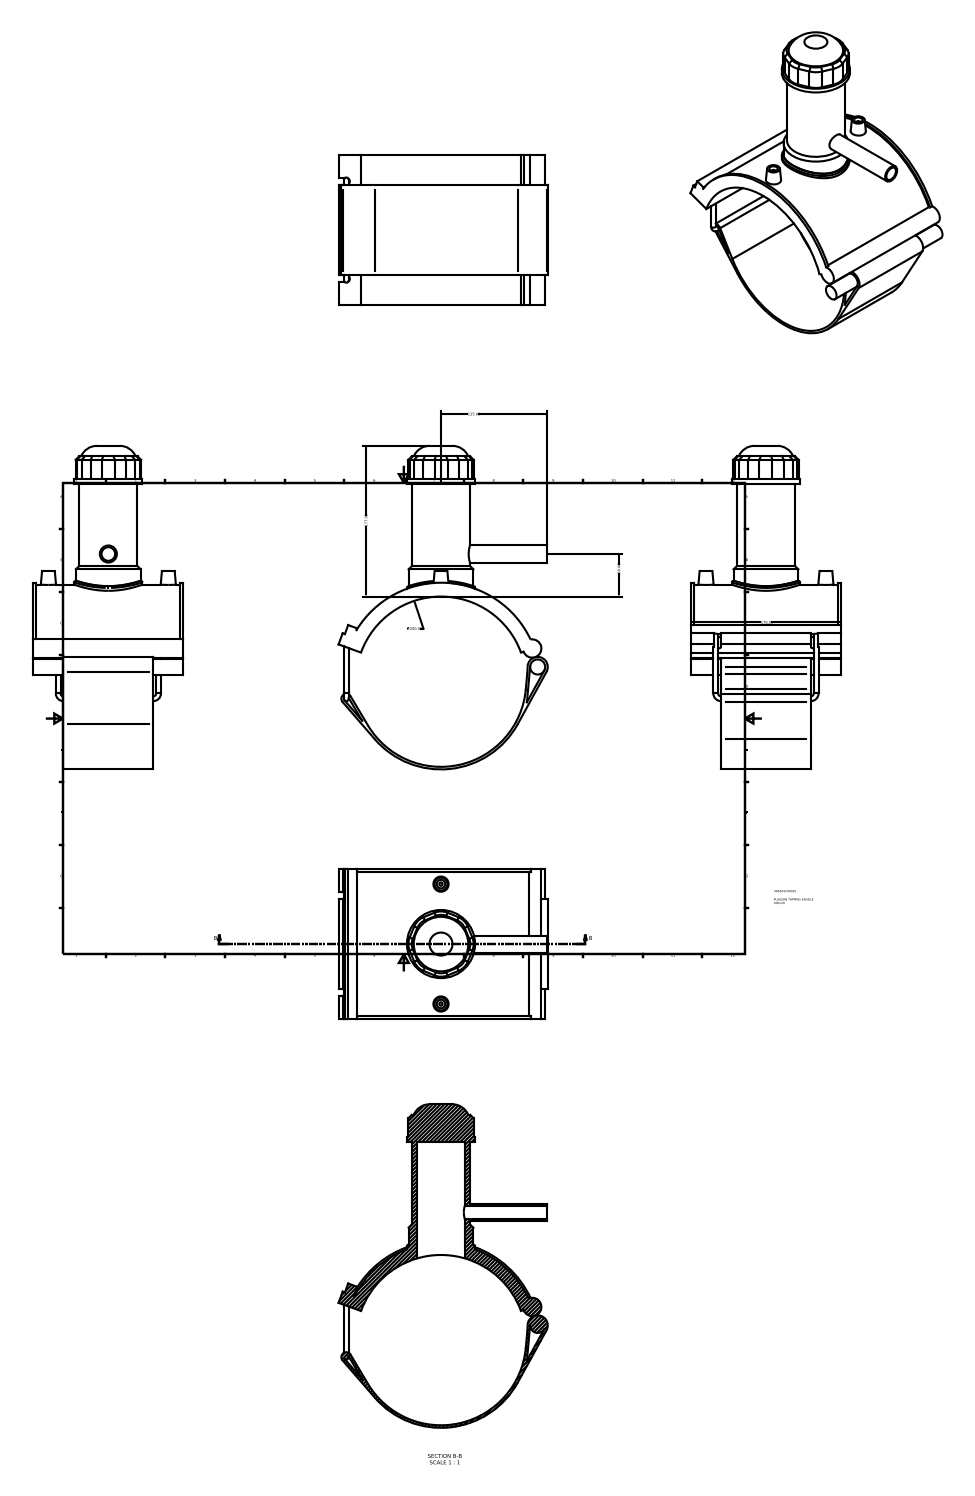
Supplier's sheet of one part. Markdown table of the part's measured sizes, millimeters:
| quantity | value |
| --- | --- |
| part name | 496304200020 |
| STEP written by | Autodesk Inventor 2015 (AUTOMOTIVE_DESIGN) |
| units | millimeters |
| bodies | 1 solid, 121 faces (68 planar, 38 cylindrical, 15 other) |
| overall size | 380 × 245.66 × 176 |
| volume | 1 264 000 mm³ |
| surface area | 299 248 mm² |
| round holes (diameter × count) | 10 × 2, 16 × 1, 56 × 1 |
| round bosses / shafts (diameter × count) | 5.6 × 2, 4 × 2, 80 × 1, 76 × 1, 68 × 1, 20 × 1, 17.69 × 1 |
| partial cylindrical surfaces (radius × count) | 20 × 8, 4.2 × 2, 100 × 2, 2.8 × 1, 5.8 × 1, 10.77 × 1, 11.85 × 1, 103 × 1 |
| main face-to-face distances | 3, 176, 3.02, 35.2, 140.8, 11.2, 14, 2.68, 25.21, 2.8 |
| hole center spacings | 70.4, 140.8 |
